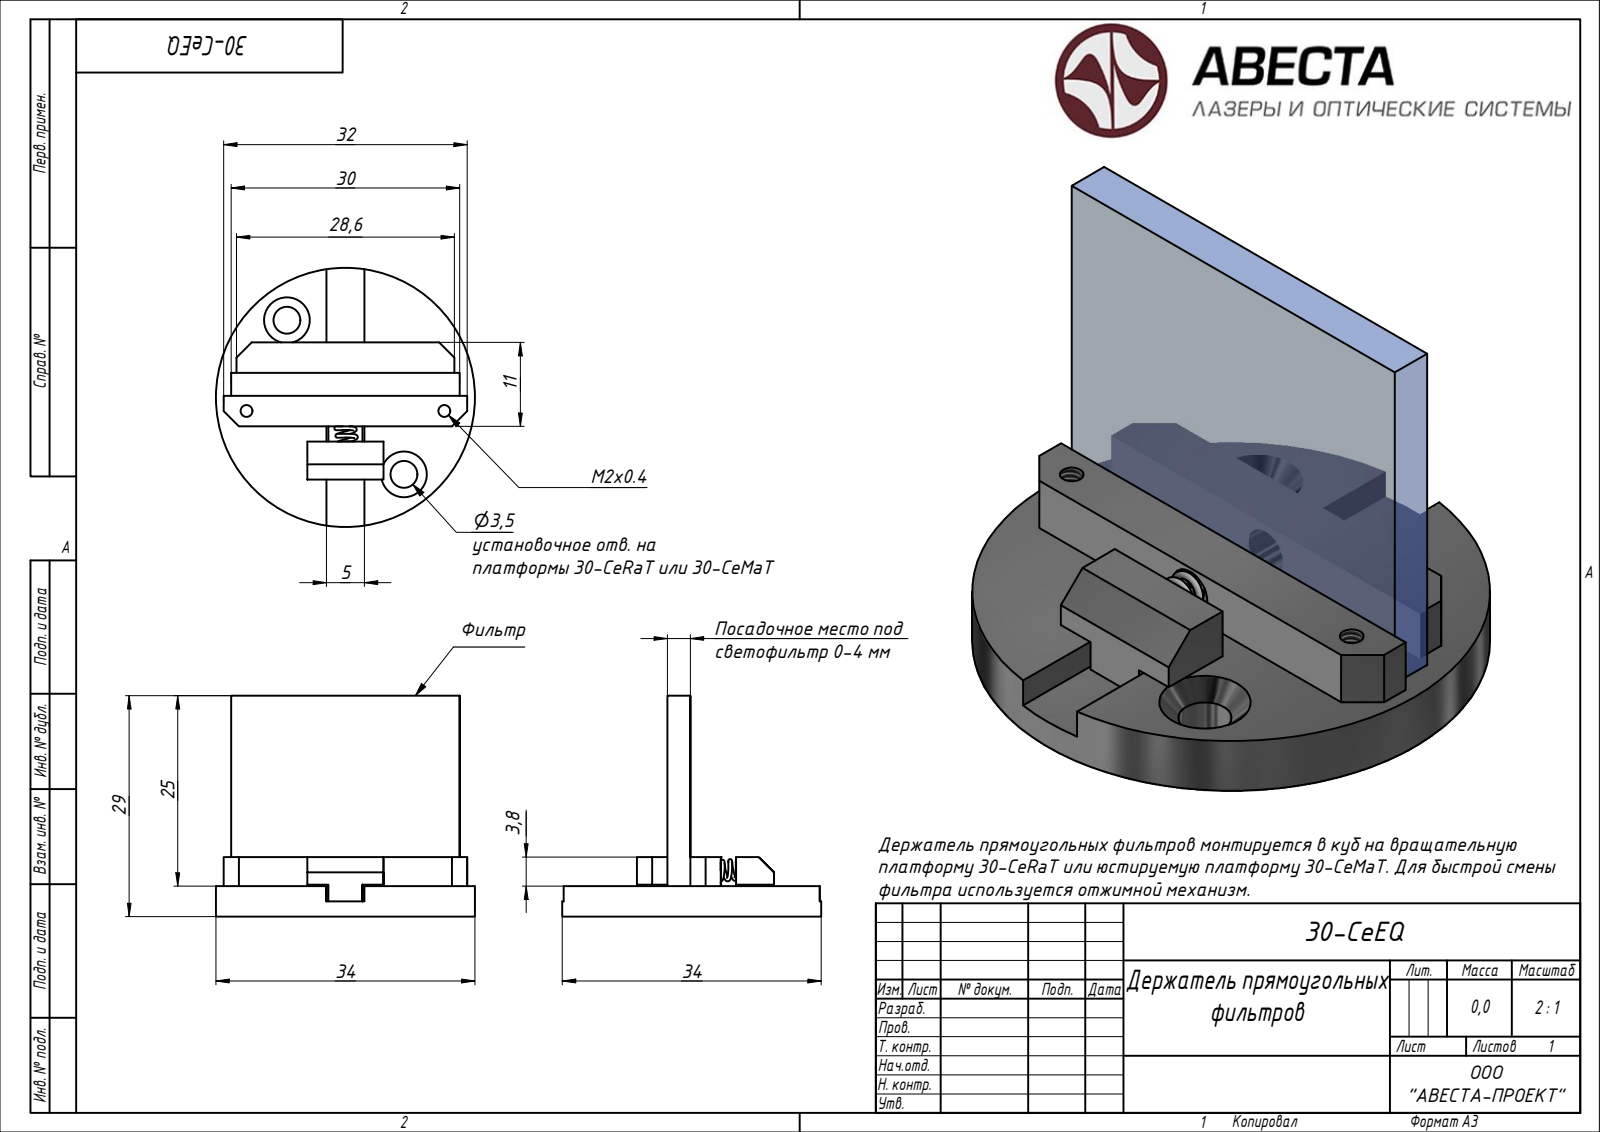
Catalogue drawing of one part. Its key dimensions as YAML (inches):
step_written_by: "ST-DEVELOPER v15 (AUTOMOTIVE_DESIGN)"
units: inches
bodies: {solids: 5, faces: 79, planar: 49, cylindrical: 0, other: 30}
overall_size: [1.339, 1.339, 1.142]
volume: 0.39
surface_area: 9.068
face_to_face_distances: [0.157, 0.118, 0.079, 0.307, 0.15, 0.276, 0.228, 0.433, 0.492, 0.689]
